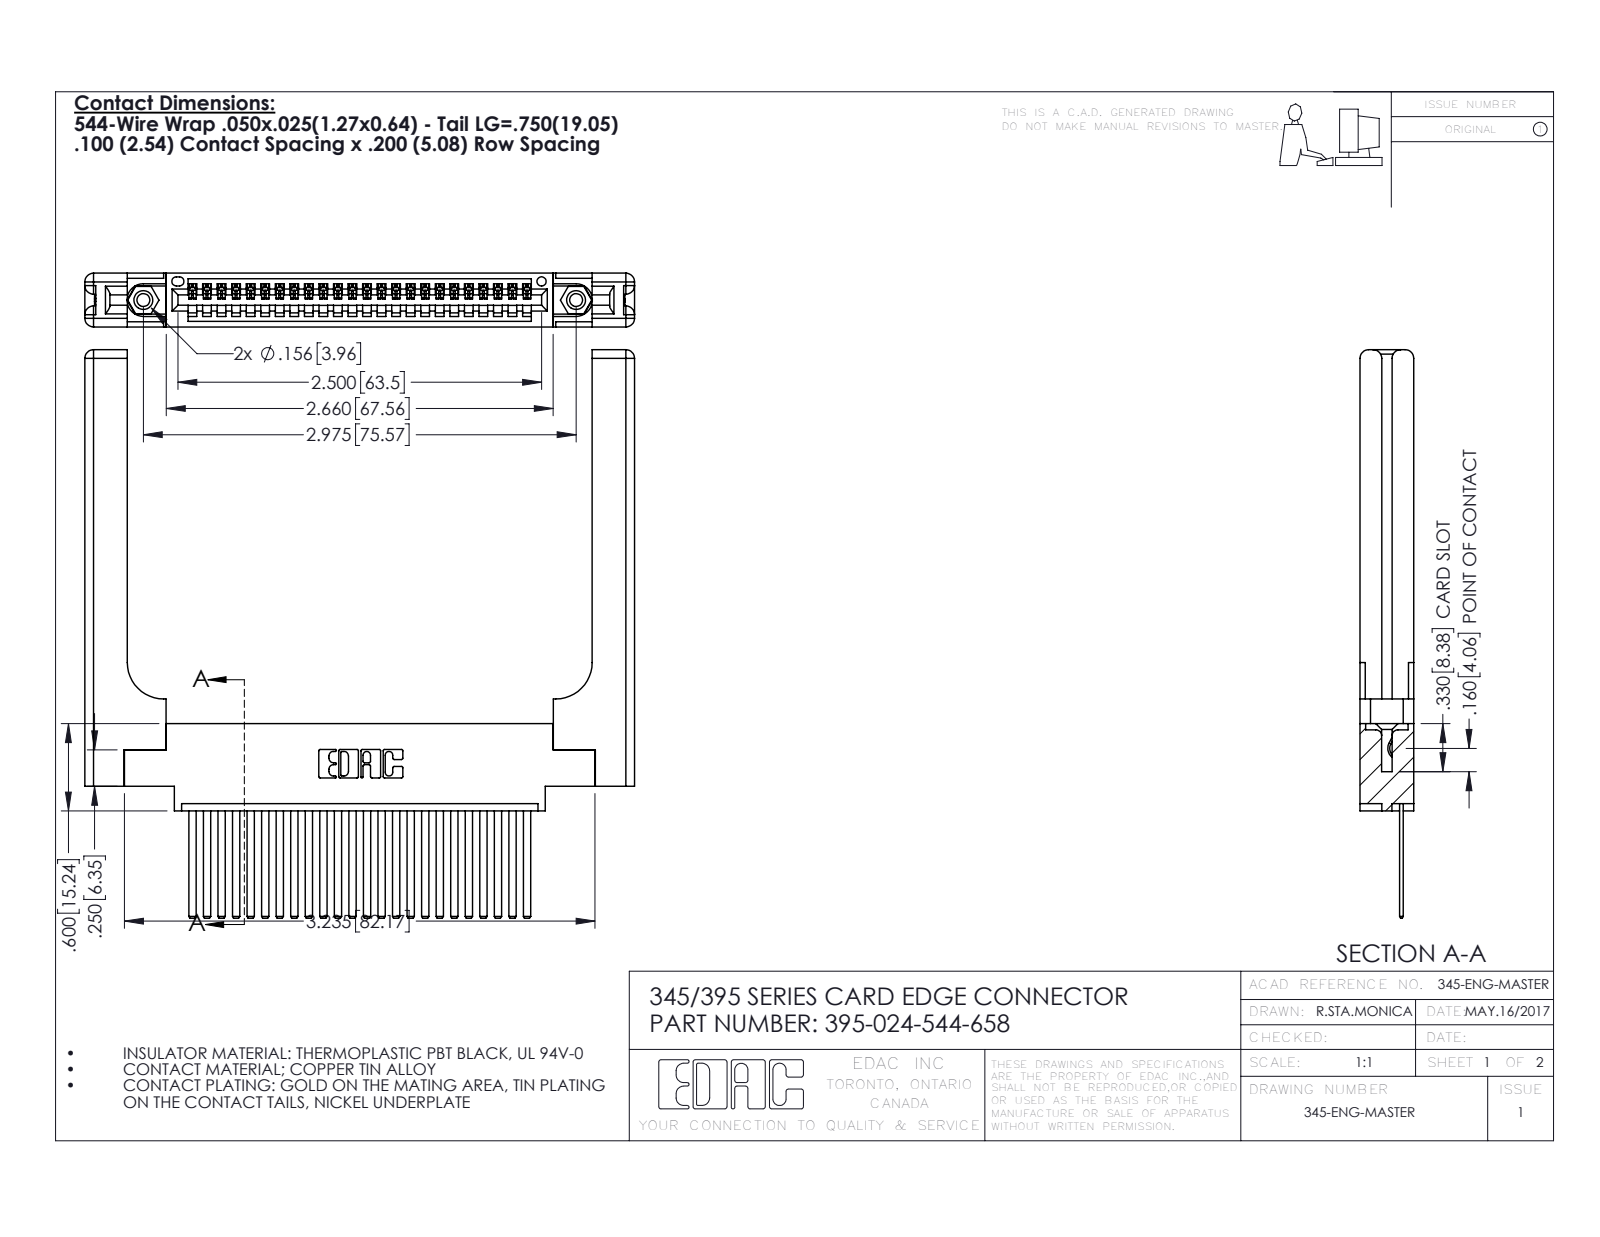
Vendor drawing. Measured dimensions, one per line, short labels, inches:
name: 345 Part_0.170 Offset - 0.156 Dia-TH; 395-024-544-658; 345-250-001_345-250-001-102; 345-220-058_345-220-058 (+1 more)
written by: SolidWorks 2016 (CONFIG_CONTROL_DESIGN)
unit: in
bodies: 29 solids, 1634 faces (1096 planar, 478 cylindrical, 60 other)
size: 3.907 × 3.779 × 0.37
volume: 1.076 in³; area: 28.15 in²
holes: 2× ⌀0.089, 2× ⌀0.125, 2× ⌀0.156, 1× ⌀0.064
bosses: 2× ⌀0.155
rounds: 48× R0.006, 22× R0.01, 16× R0.06, 6× R0.007, 6× R0.031, 3× R0.026, 2× R0.03, 2× R0.031
face distances: 0.37, 0.072, 0.298, 0.098, 0.272, 0.025, 0.148, 0.15, 0.077, 0.2
hole spacings: 0.27, 2.741, 2.975
